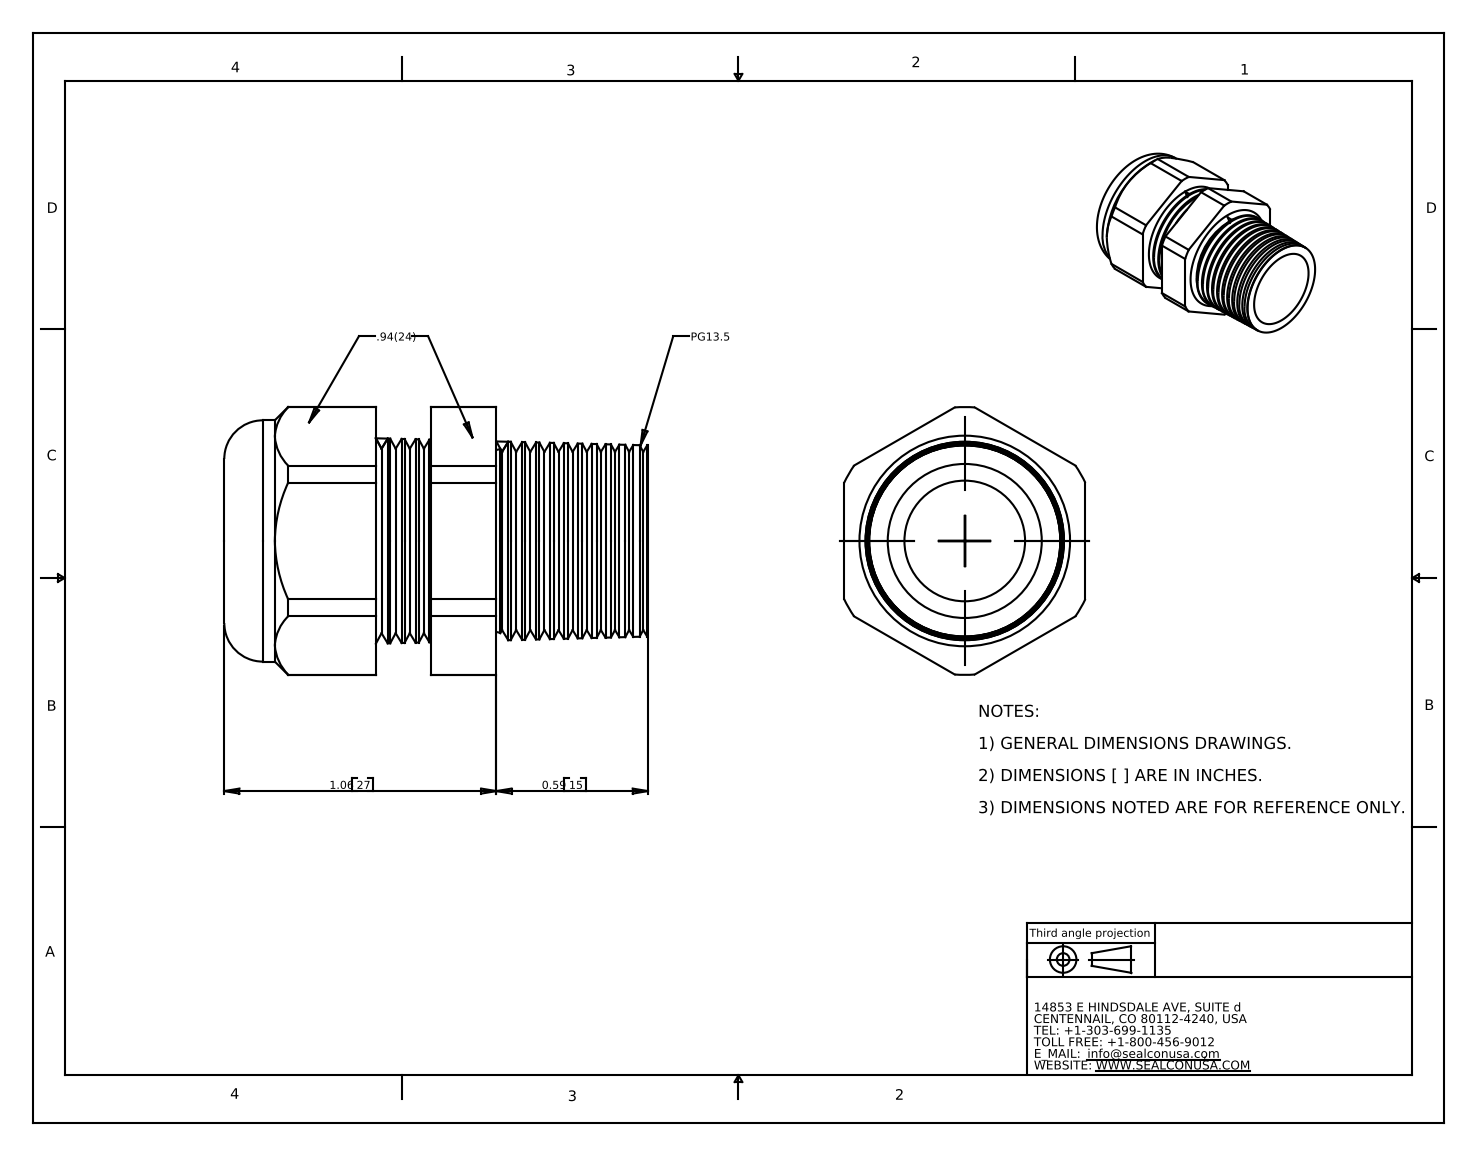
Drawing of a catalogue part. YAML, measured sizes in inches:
part_name: "CD13CA-GY"
step_written_by: "SolidWorks 2007 (CONFIG_CONTROL_DESIGN)"
units: inches
bodies: {solids: 2, faces: 148, planar: 20, cylindrical: 22, other: 106}
overall_size: [1.65, 1.043, 0.94]
volume: 0.617
surface_area: 10.82
round_holes:
  - {diameter: 0.47, count: 1}
  - {diameter: 0.6, count: 1}
round_bosses_or_shafts:
  - {diameter: 0.94, count: 1}
partial_cylinders:
  - {radius: 0.522, count: 1}
face_to_face_distances: [0.94, 0.214, 0.47, 0.256, 0.394, 0.607, 0.863, 1.453, 1.059, 0.846]
